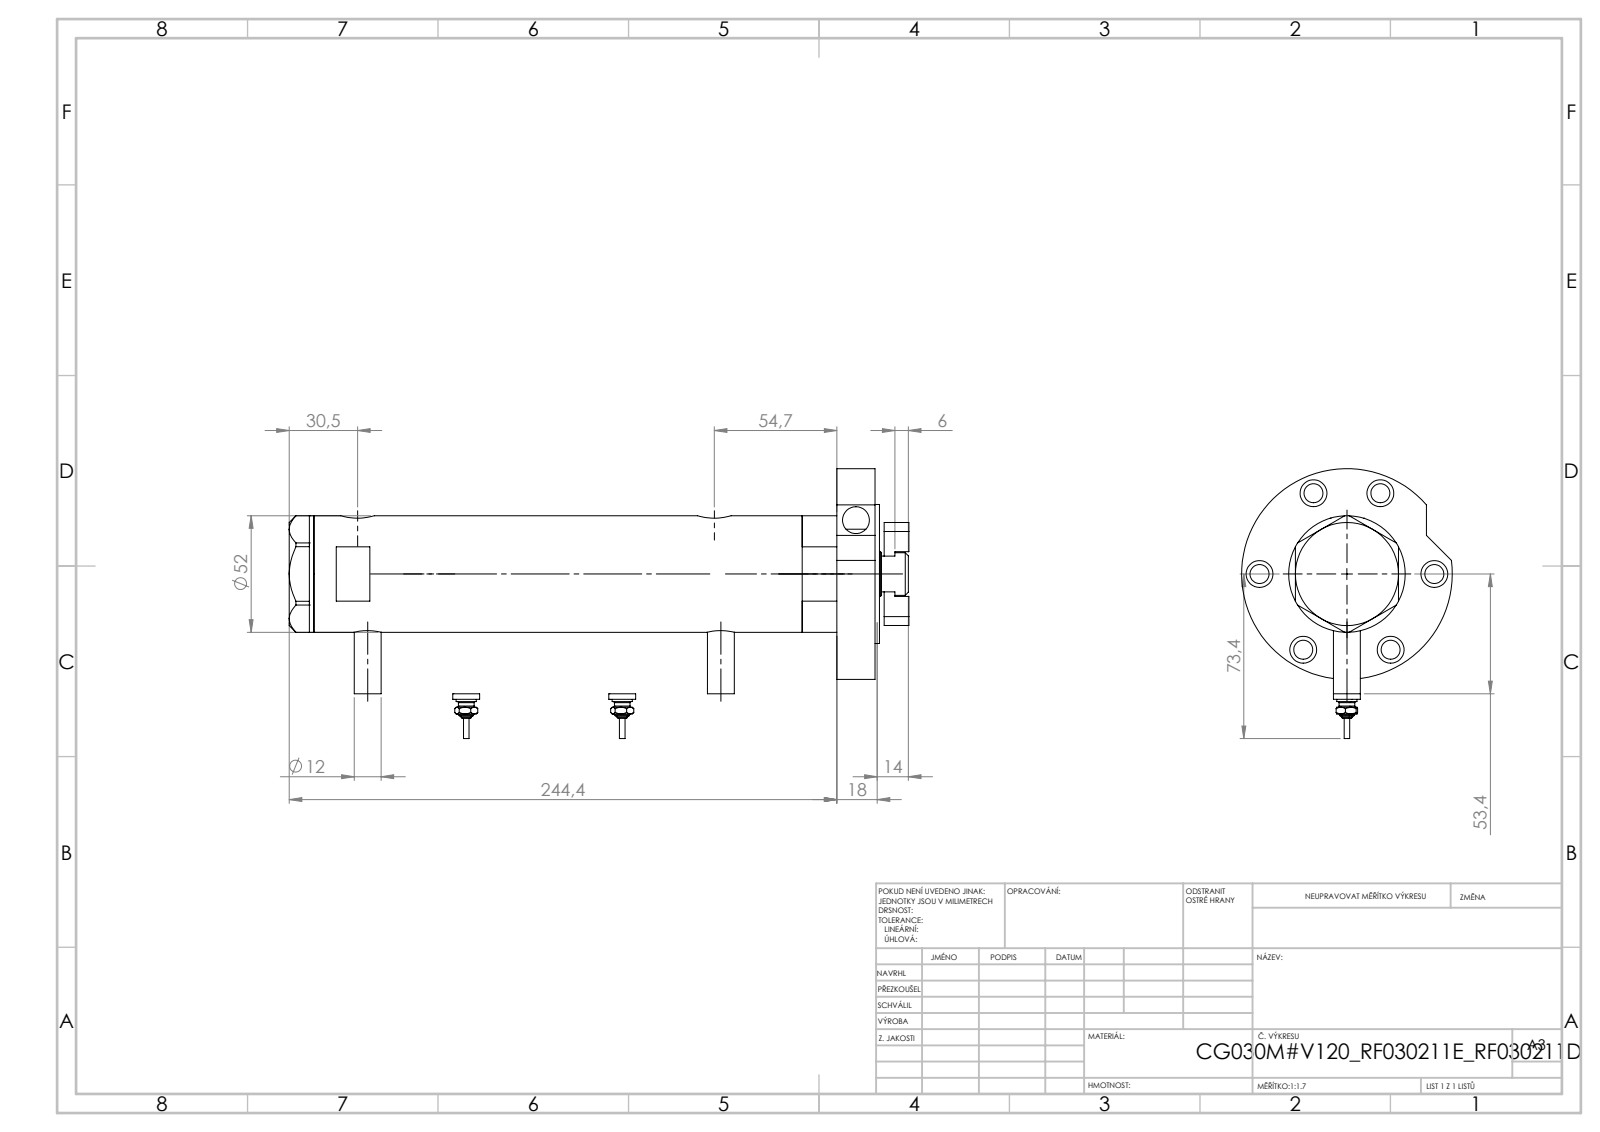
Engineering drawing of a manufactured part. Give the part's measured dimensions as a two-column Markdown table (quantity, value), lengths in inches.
| quantity | value |
| --- | --- |
| part name | V270CG_BACK; V270CG_RF211D; V270CG_MIDDLE; Switch (+3 more) |
| STEP written by | SolidWorks 2019 (CONFIG_CONTROL_DESIGN) |
| units | inches |
| bodies | 9 solids, 310 faces (128 planar, 118 cylindrical, 64 other) |
| overall size | 10.886 × 4.74 × 3.701 |
| volume | 35.65 in³ |
| surface area | 211 in² |
| round holes (diameter × count) | 0.472 × 7, 0.335 × 6, 0.201 × 4, 0.354 × 4, 0.383 × 2, 0.492 × 2, 0.591 × 2, 0.256 × 1, 0.787 × 1, 0.846 × 1, 1.181 × 1, 1.299 × 1 |
| round bosses / shafts (diameter × count) | 0.472 × 4, 0.354 × 2, 0.276 × 2, 0.177 × 2, 0.098 × 2, 3.701 × 1, 2.441 × 1, 2.047 × 1 |
| main face-to-face distances | 0.669, 9.189, 9.858, 0.079, 9.937, 0.433, 7.146, 2.043, 2.713, 2.791 |
| hole center spacings | 1.535, 0.659, 1.479, 1.843, 0.394, 0.881, 0.904, 1.113 |
